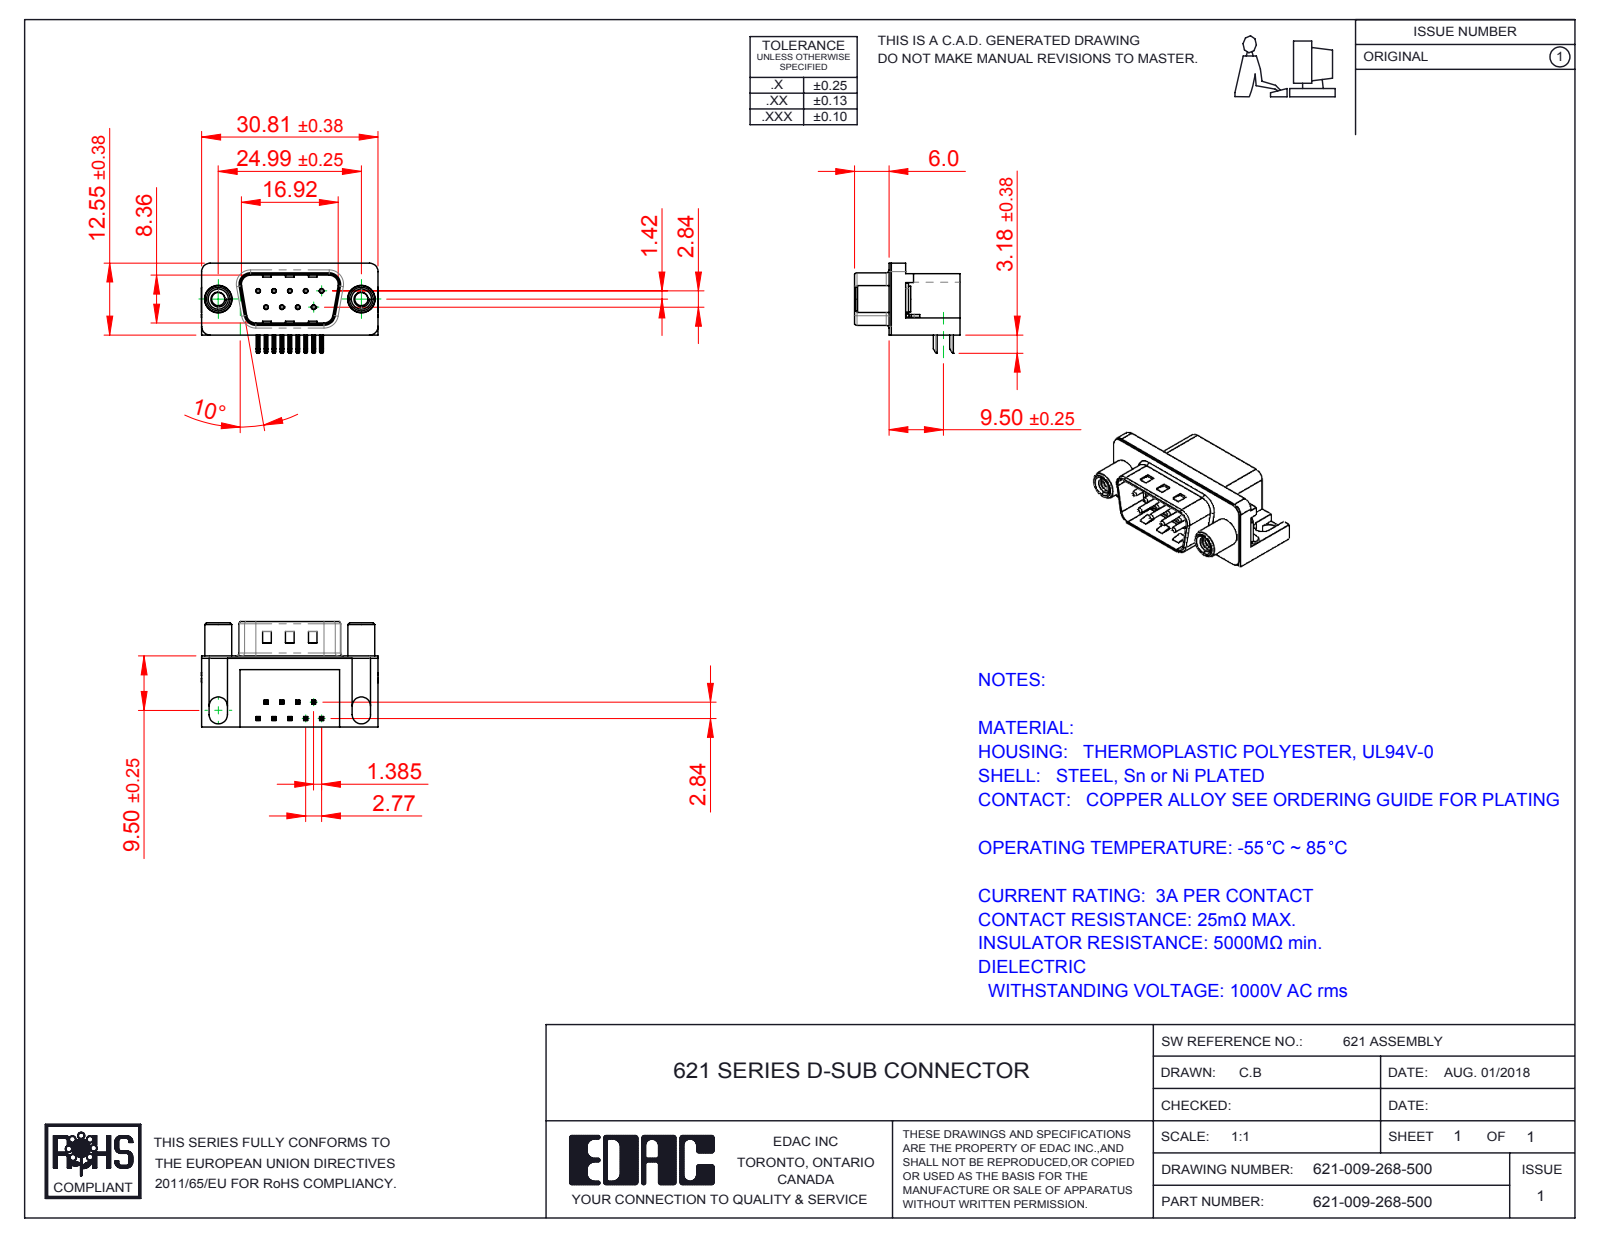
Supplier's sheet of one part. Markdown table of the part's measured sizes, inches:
| quantity | value |
| --- | --- |
| part name | 621 Housing_9 Socket; 621 Shell_9 Socket; 621 Non Board Mount; 621 Contact Bottom (+3 more) |
| STEP written by | SolidWorks 2016 (CONFIG_CONTROL_DESIGN) |
| units | inches |
| bodies | 15 solids, 979 faces (563 planar, 319 cylindrical, 97 other) |
| overall size | 1.216 × 0.724 × 0.619 |
| volume | 0.201 in³ |
| surface area | 6.893 in² |
| round holes (diameter × count) | 0.014 × 9, 0.031 × 9, 0.091 × 2, 0.122 × 2, 0.157 × 2, 0.189 × 2, 0.197 × 2 |
| round bosses / shafts (diameter × count) | 0.03 × 9, 0.193 × 2, 0.185 × 2, 0.177 × 2, 0.152 × 2 |
| partial cylindrical surfaces (radius × count) | 0.01 × 36, 0.005 × 18, 0.039 × 16, 0.02 × 9, 0.059 × 8, 0.063 × 8, 0.035 × 4, 0.079 × 4 |
| main face-to-face distances | 0.016, 0.472, 0.488, 0.407, 0.114, 0.374, 0.098, 0.083, 0.014, 0.421 |
| hole center spacings | 0.124, 0.109, 0.218, 0.198, 0.198, 0.327, 0.294, 0.295 |
